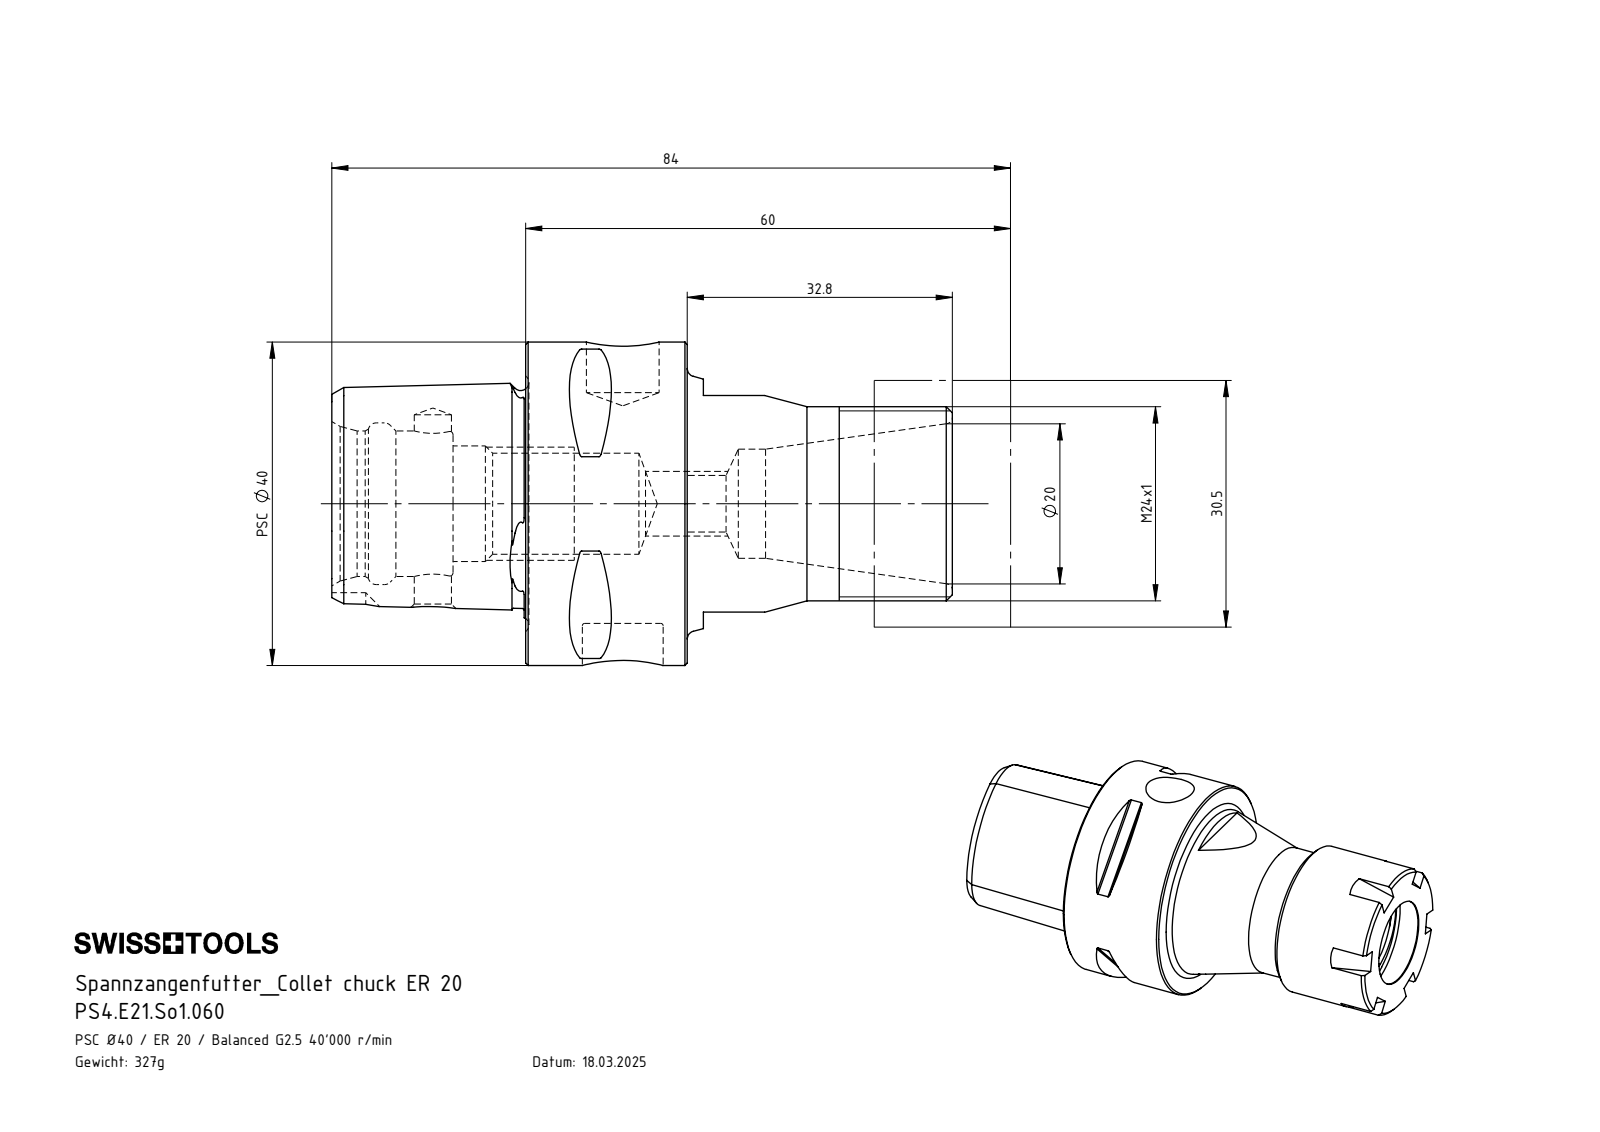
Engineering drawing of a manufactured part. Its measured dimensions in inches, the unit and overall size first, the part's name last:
Units: inches
Overall size (bounding box): 3.248 × 1.138 × 1.102
Round holes (diameter × count): ⌀0.626 ×1, ⌀0.906 ×1, ⌀0.984 ×1
Round bosses / shafts (diameter × count): ⌀1.102 ×1
Partial cylindrical surfaces — rounded edges, fillets, slot ends (radius × count): R0.378 ×2
Main face-to-face distances: 0.748, 0.472, 0.276, 0.157, 0.506, 0.033, 0.242, 0.157, 0.158, 0.756
Volume: 0.24 in³ · Surface area: 6.758 in²
Bodies: 1 solid, 75 faces (24 planar, 28 cylindrical, 23 other)
Part name (STEP PRODUCT): E21-ER1.001.019; PS4.E21.So1.060; PS4-E21.So1.060_A_Fertigbearbeitung
STEP written by: SolidWorks 2022 (AUTOMOTIVE_DESIGN)
